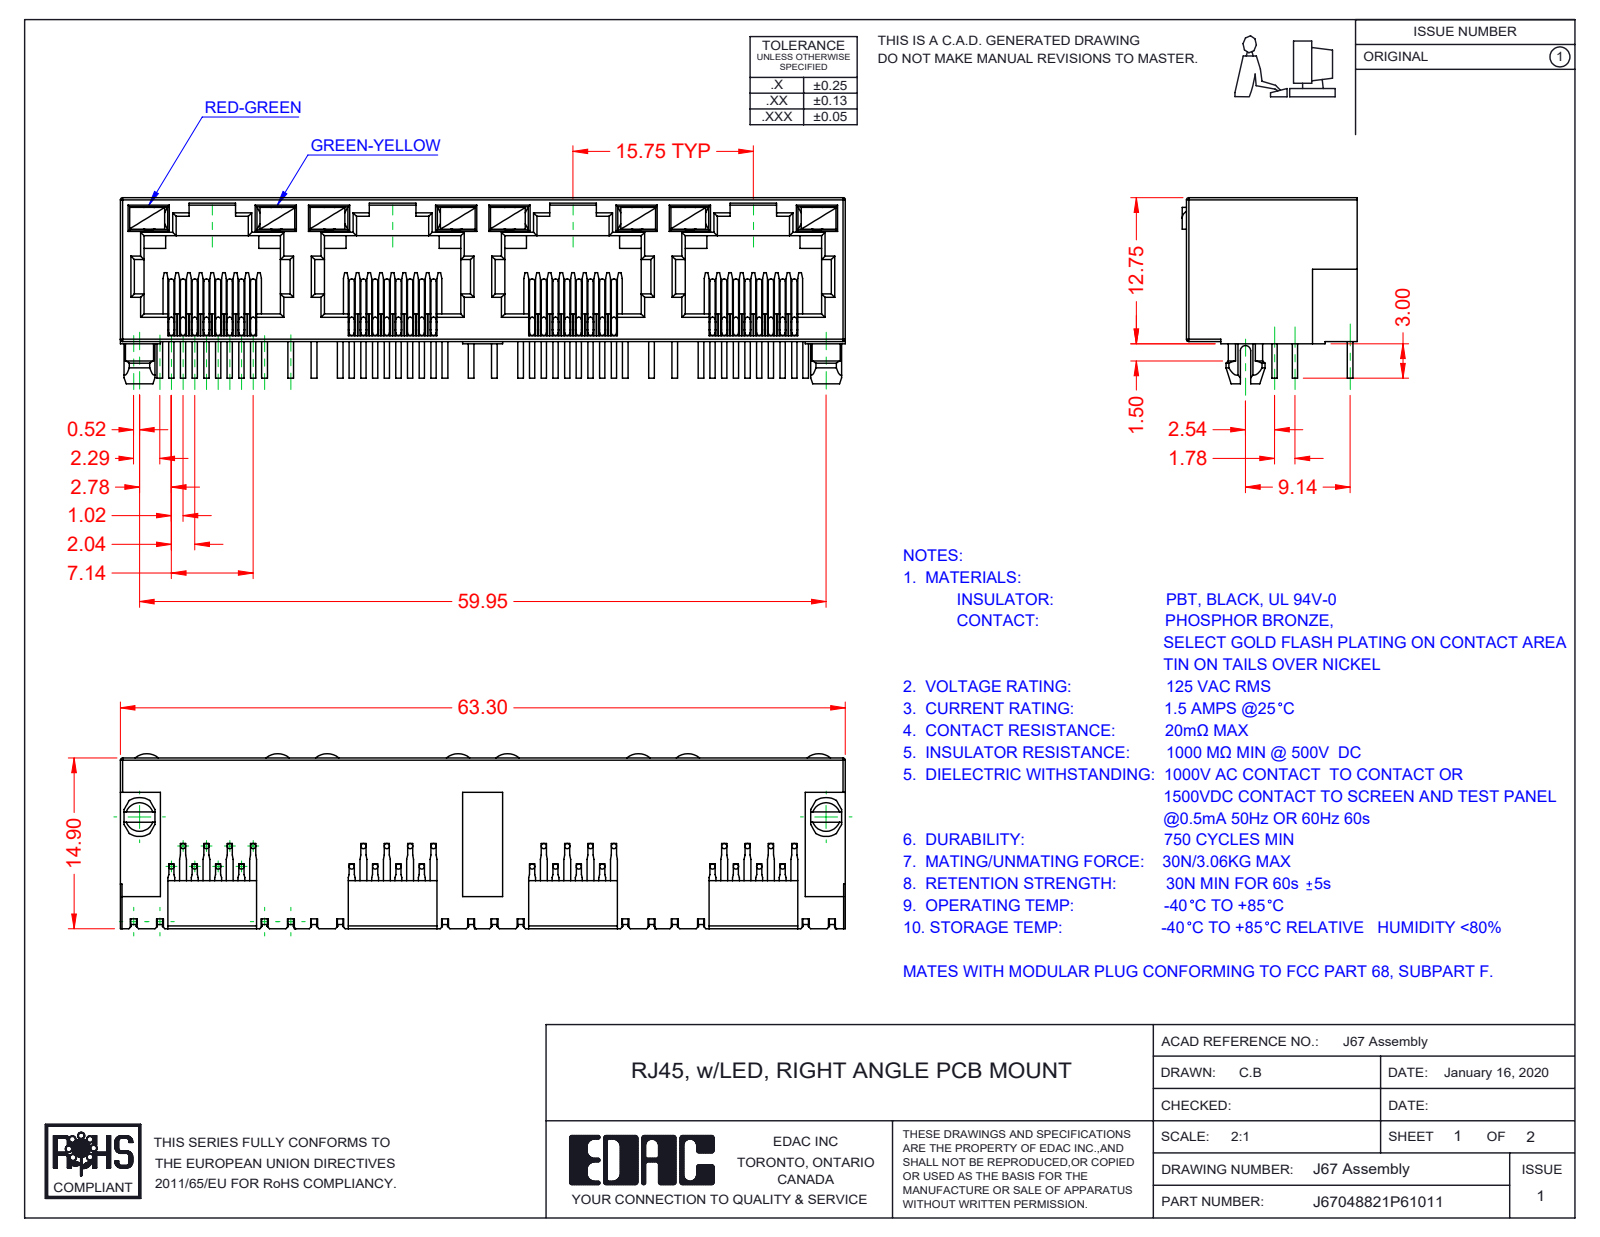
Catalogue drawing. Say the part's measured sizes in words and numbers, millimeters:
The part is named "67 Insulator; 67 Contacts; J67048822P65011; 67 LED LH_6-Red-Green (+1 more)". Its 3-D file was written by "SolidWorks 2016 (CONFIG_CONTROL_DESIGN)". It is 41 solids with 2481 faces: 1781 planar, 492 cylindrical and 208 other. Overall it measures 63.3 by 16.25 by 15.28 millimeters. Its volume is 5 159 cubic millimeters and its surface area 11 573 square millimeters. Round bosses or shafts: 96 of diameter 0.46. Partial cylindrical surfaces (rounded edges, fillets, slot ends): 66 of radius 0.2, 29 of radius 0.3, 9 of radius 0.45, 8 of radius 1.55, 2 of radius 1.5, 2 of radius 1.7, 1 of radius 0.35, 1 of radius 1. The main face-to-face distances are 0.5, 12.55, 1.89, 0.89, 10, 15.75, 1, 1.39, 11, 11.89.
